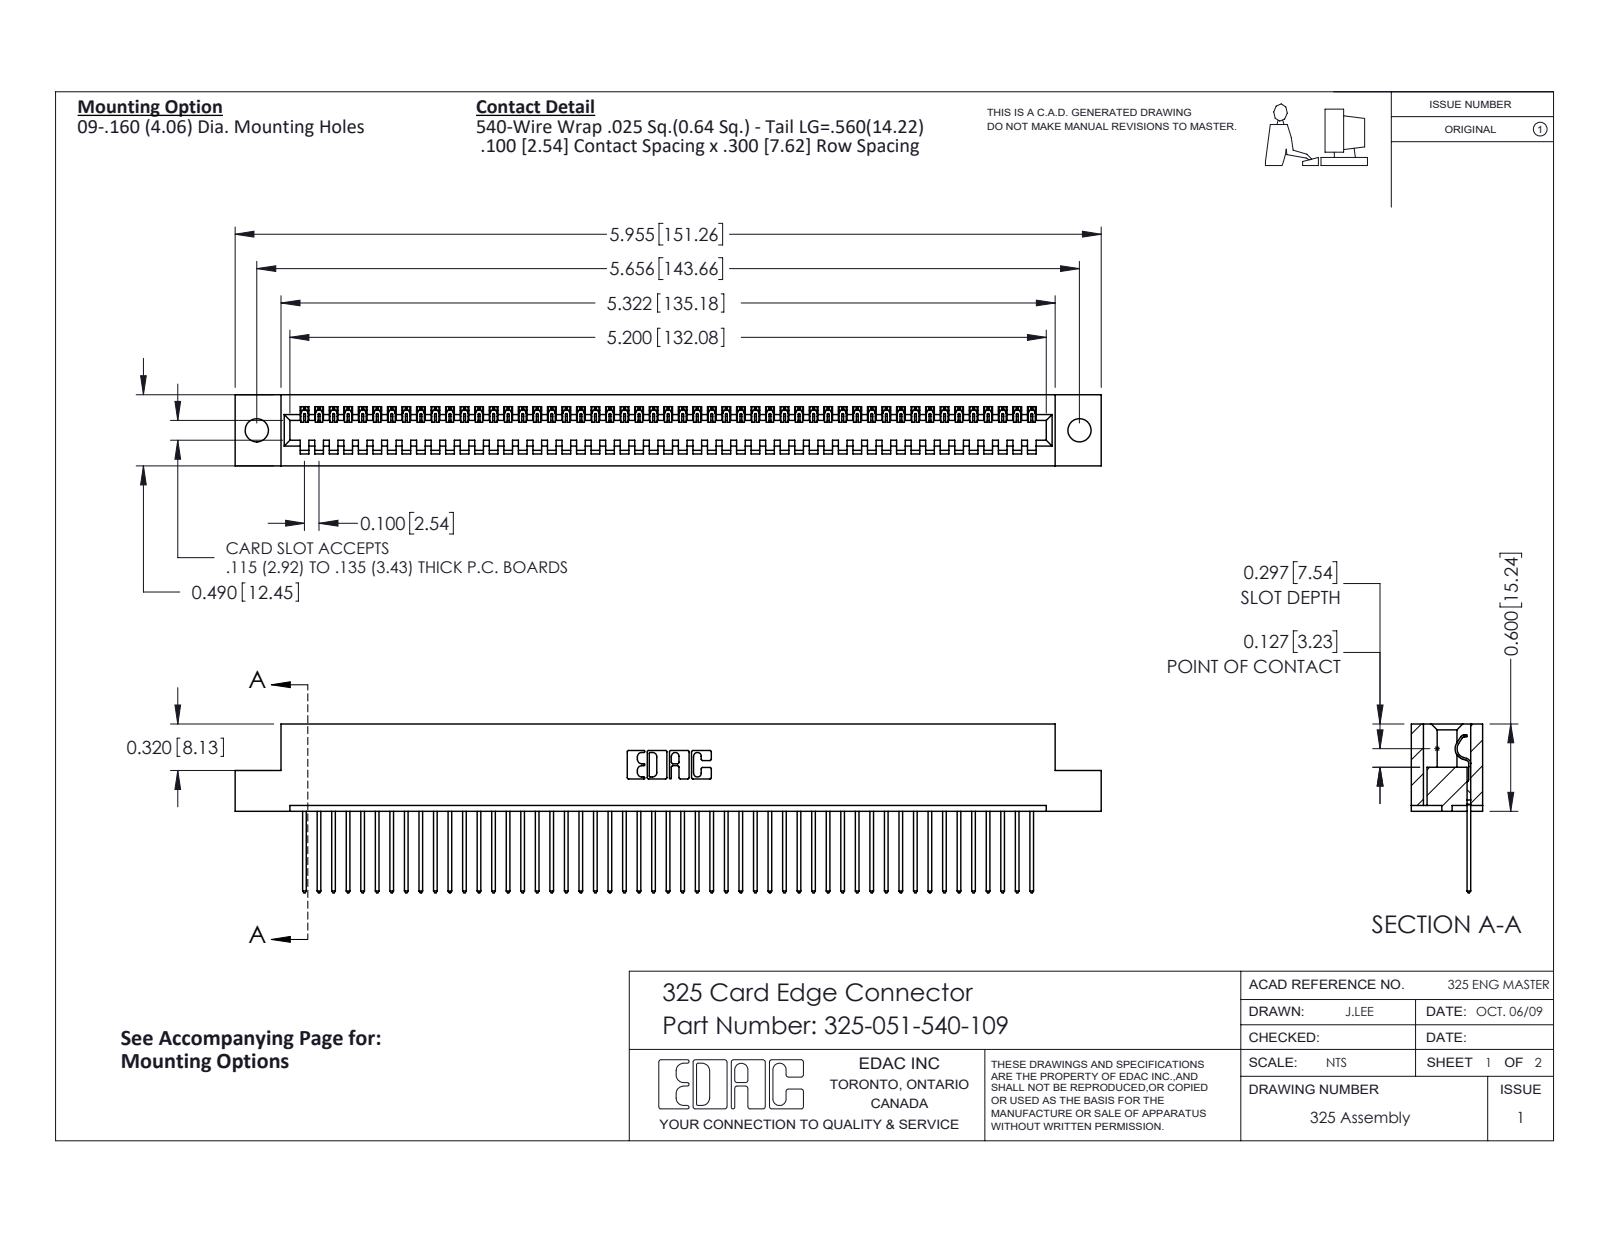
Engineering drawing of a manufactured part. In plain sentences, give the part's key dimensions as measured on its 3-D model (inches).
The part is named "325-051-540-109; 325-292-001_325-293-140; 325 Part_.160 TH". Its 3-D file was written by "SolidWorks 2016 (CONFIG_CONTROL_DESIGN)". It is 52 solids with 3072 faces: 2212 planar, 860 cylindrical and 0 other. Overall it measures 5.955 by 1.16 by 0.49 inches. Its volume is 1.166 cubic inches and its surface area 33.23 square inches. Round holes: 2 of diameter 0.16. Partial cylindrical surfaces (rounded edges, fillets, slot ends): 102 of radius 0.006, 102 of radius 0.01, 22 of radius 0.01, 6 of radius 0.007, 6 of radius 0.031, 3 of radius 0.026, 1 of radius 0.014, 1 of radius 0.022. The main face-to-face distances are 0.083, 0.407, 0.49, 0.3, 0.107, 0.383, 0.025, 0.325, 0.56, 0.263. The hole center spacings are 5.656.
